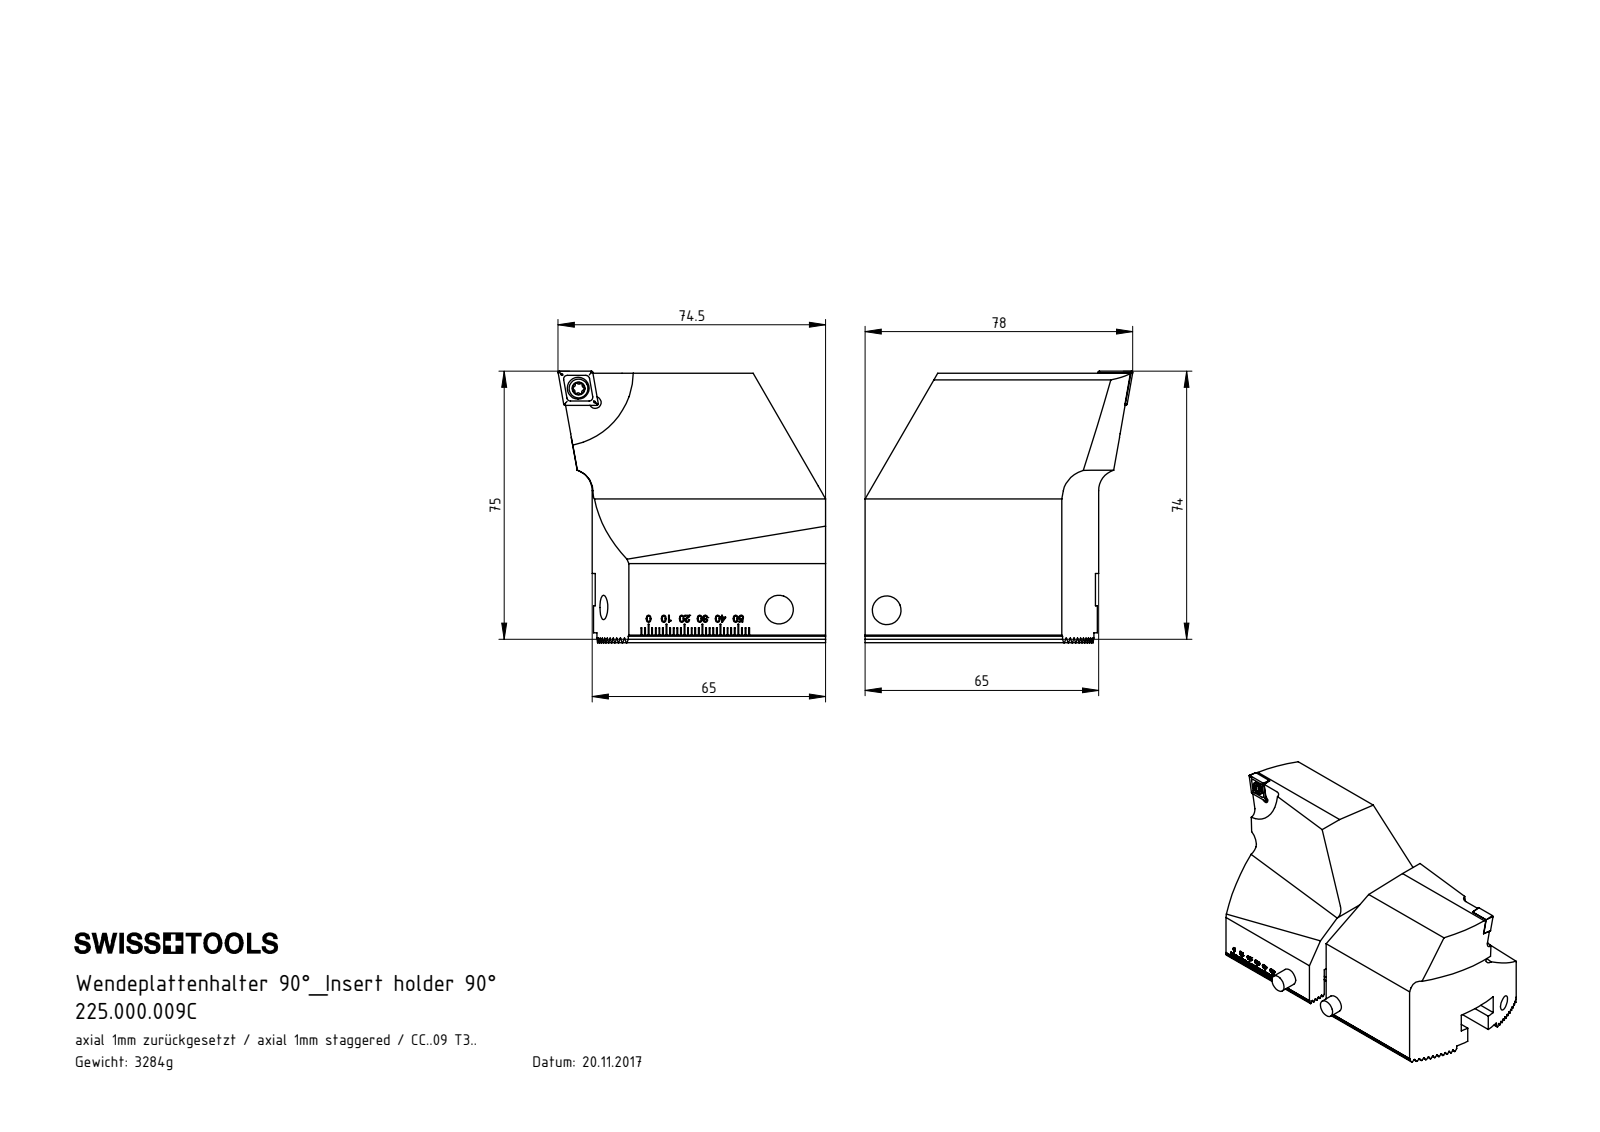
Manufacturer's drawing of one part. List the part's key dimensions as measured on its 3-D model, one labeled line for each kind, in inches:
Part name (STEP PRODUCT): ISO 4028 - M8 x 35; ISO 8734 - 8 x 20 m6; CCMT09T304; WCB-ER2.001.009_A (+3 more)
STEP written by: SolidWorks 2017 (CONFIG_CONTROL_DESIGN)
Units: inches
Bodies: 12 solids, 1132 faces (686 planar, 140 cylindrical, 306 other)
Overall size (bounding box): 6.299 × 3.449 × 2.975
Volume: 25.65 in³ · Surface area: 99.95 in²
Round holes (diameter × count): ⌀0.13 ×4, ⌀0.315 ×4, ⌀0.173 ×2, ⌀0.24 ×2, ⌀0.268 ×2
Round bosses / shafts (diameter × count): ⌀0.315 ×2, ⌀0.217 ×2, ⌀0.207 ×2, ⌀0.157 ×2
Partial cylindrical surfaces — rounded edges, fillets, slot ends (radius × count): R0.006 ×22, R0.013 ×12, R0.023 ×12, R0.157 ×2, R0.207 ×2, R0.827 ×2, R2.559 ×2, R2.717 ×2
Main face-to-face distances: 0.068, 0.341, 0.136, 2.756, 0.273, 0.205, 1.705, 0.965, 1.791, 0.409
Hole centre spacings: 0.239, 0.244, 0.276, 1.181, 3.034, 3.229, 3.27, 3.275
